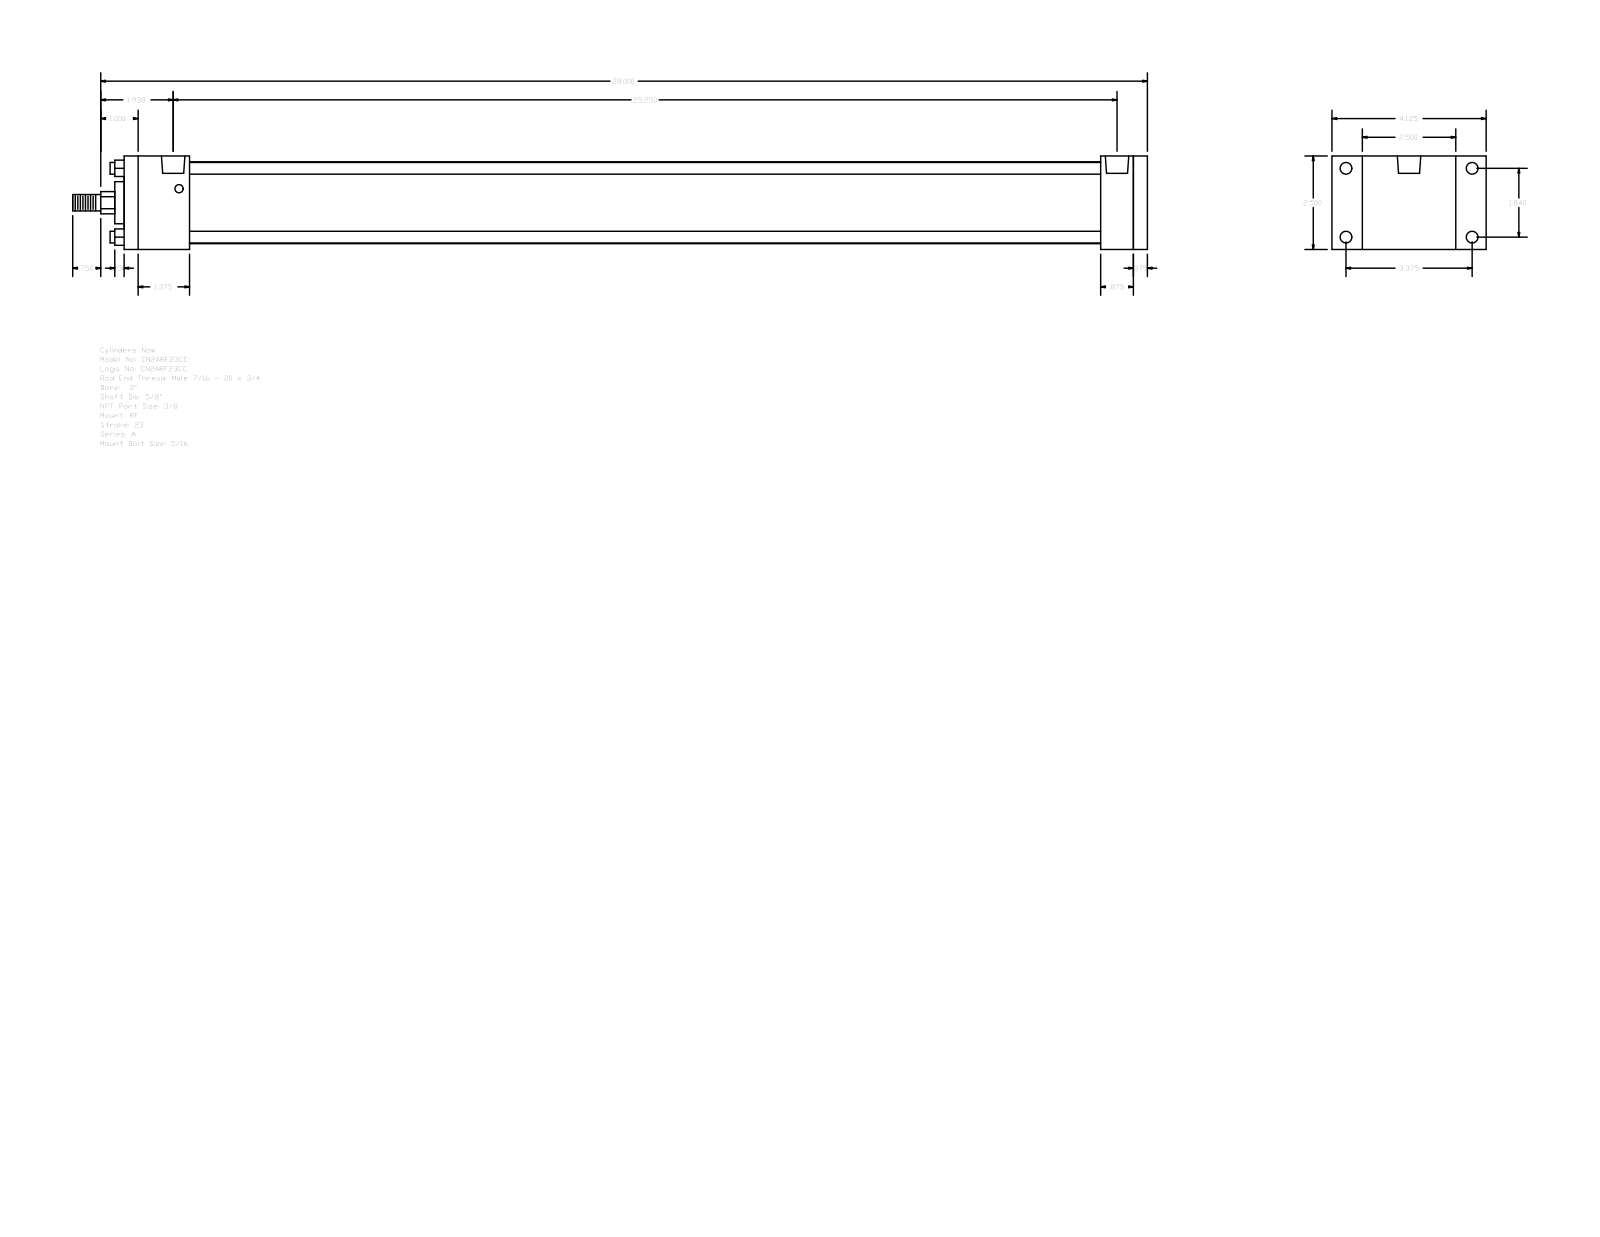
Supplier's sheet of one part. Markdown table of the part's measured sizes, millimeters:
| quantity | value |
| --- | --- |
| part name | A_RF__0200_0.625 |
| STEP written by | GSSL Pune (CONFIG_CONTROL_DESIGN) |
| units | millimeters |
| bodies | 0 solids, 92 faces (64 planar, 28 cylindrical, 0 other) |
| overall size | 730.25 × 104.78 × 63.5 |
| round holes (diameter × count) | 5.56 × 4, 7.94 × 4, 15.93 × 2 |
| round bosses / shafts (diameter × count) | 7.94 × 4, 55.63 × 1, 28.57 × 1, 15.88 × 1, 11.11 × 1 |
| partial cylindrical surfaces (radius × count) | 7.54 × 1 |
| main face-to-face distances | 63.5, 695.32, 9.53, 685.79, 44.45, 641.34, 650.87, 663.57, 619.12, 22.22 |
| hole center spacings | 46.74, 85.72, 97.63, 633.4, 3.97, 3.98, 637.37, 637.38 |
